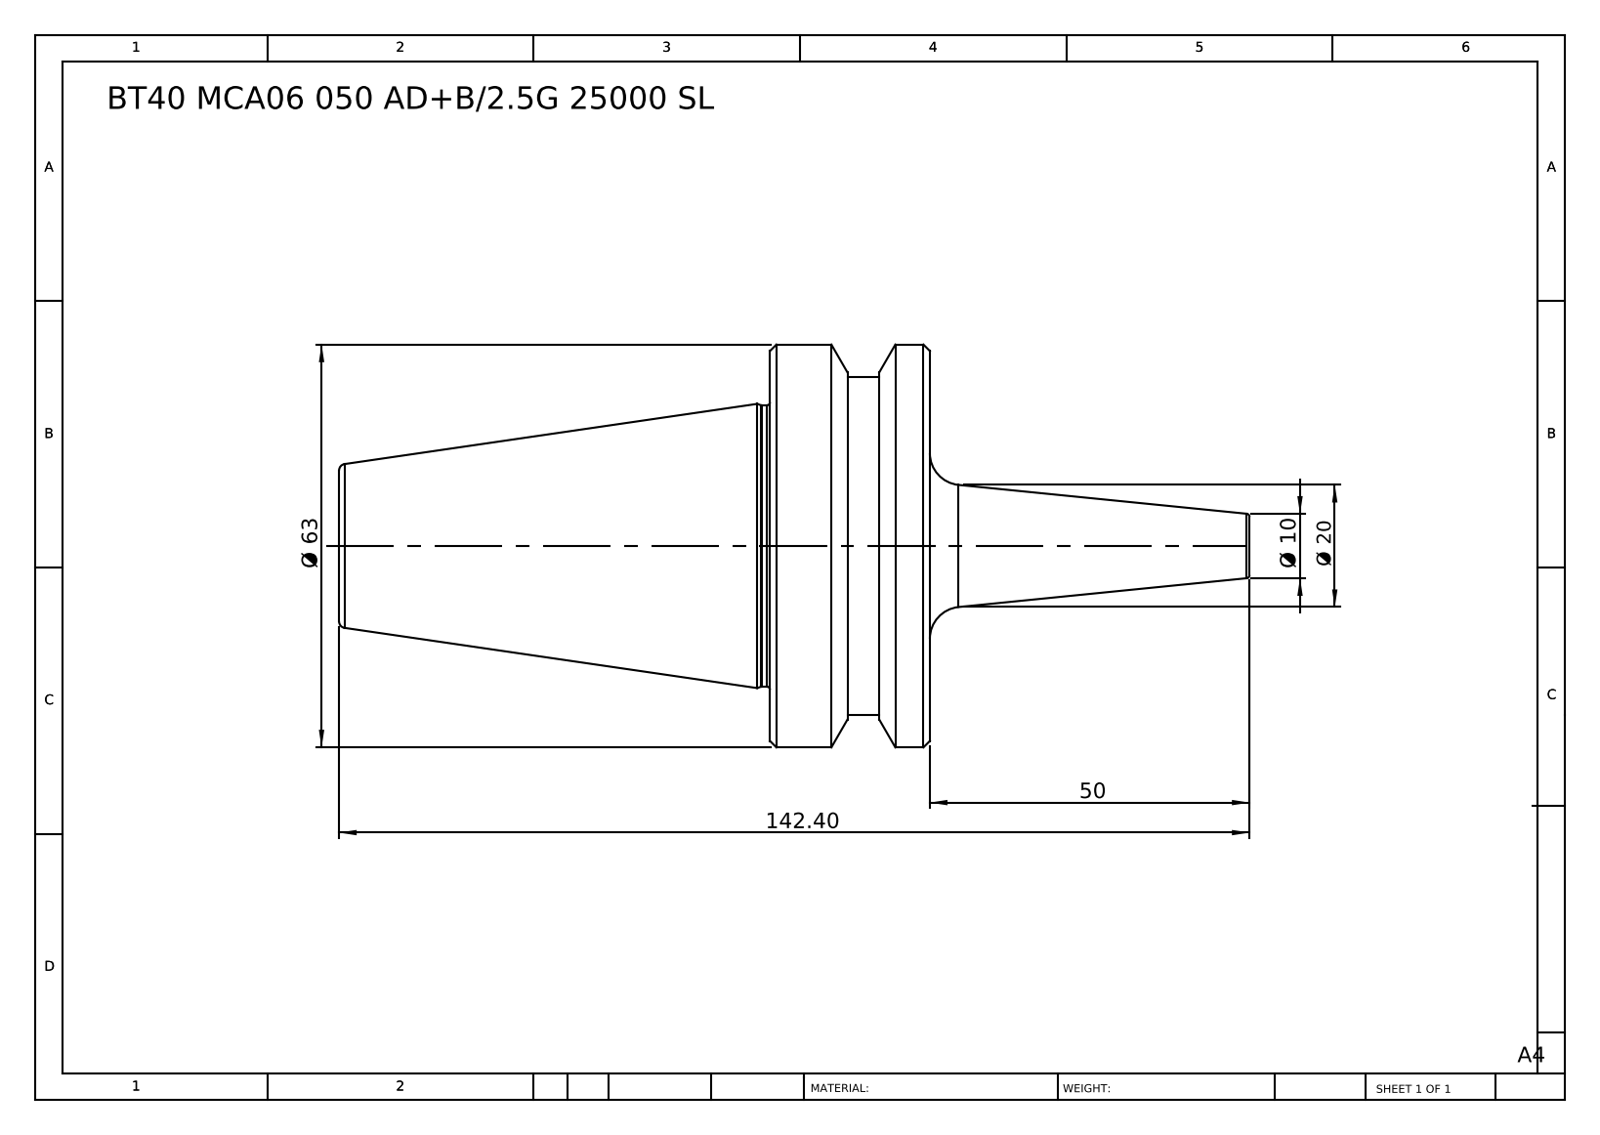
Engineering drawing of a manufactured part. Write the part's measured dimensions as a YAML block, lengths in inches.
part_name: "BT40 MCA06 050 AD+B-2.5G 25000 SL"
step_written_by: "SolidWorks 2014 (CONFIG_CONTROL_DESIGN)"
units: inches
bodies: {solids: 1, faces: 38, planar: 6, cylindrical: 8, other: 24}
overall_size: [5.606, 2.48, 2.48]
volume: 9.019
surface_area: 31.56
round_bosses_or_shafts:
  - {diameter: 2.48, count: 1}
  - {diameter: 2.087, count: 1}
  - {diameter: 1.732, count: 1}
face_to_face_distances: [0.984, 3.638, 2.654, 0.508, 0.476, 3.13, 0.311, 0.197, 0.673, 3.327]
